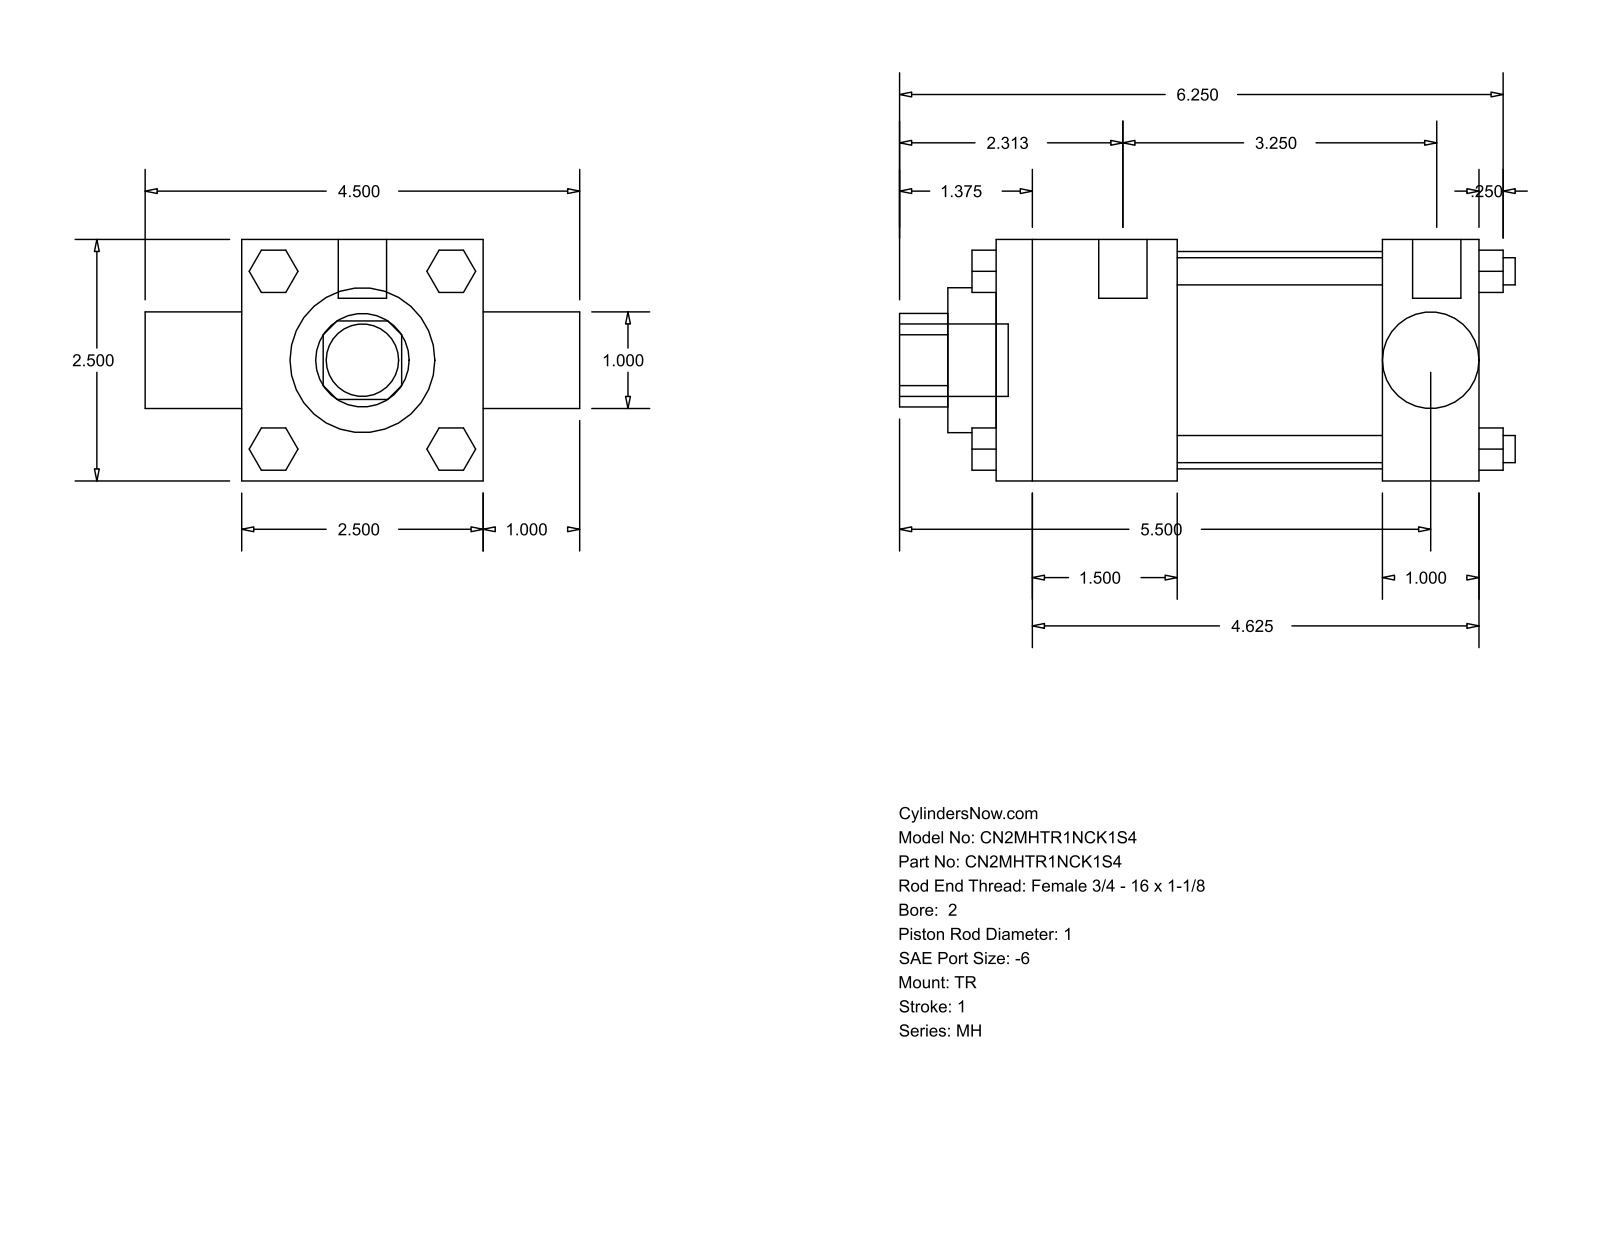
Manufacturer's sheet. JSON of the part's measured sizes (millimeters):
{"part_name": "MH_TR__0200_1", "step_written_by": "GSSL Pune (CONFIG_CONTROL_DESIGN)", "units": "millimeters", "bodies": {"solids": 0, "faces": 120, "planar": 92, "cylindrical": 28, "other": 0}, "overall_size": [161.93, 114.3, 63.5], "round_holes": [[25.35, 1], [25.4, 1], [38.1, 1], [57.15, 1]], "round_bosses_or_shafts": [[7.14, 4], [5.56, 3], [12.7, 2], [19.05, 1]], "partial_cylinders_radius": [[12.29, 1]], "face_to_face_distances": [63.5, 127, 25.4, 47.63, 101.6, 53.97, 79.37, 88.9, 114.3, 139.7]}
